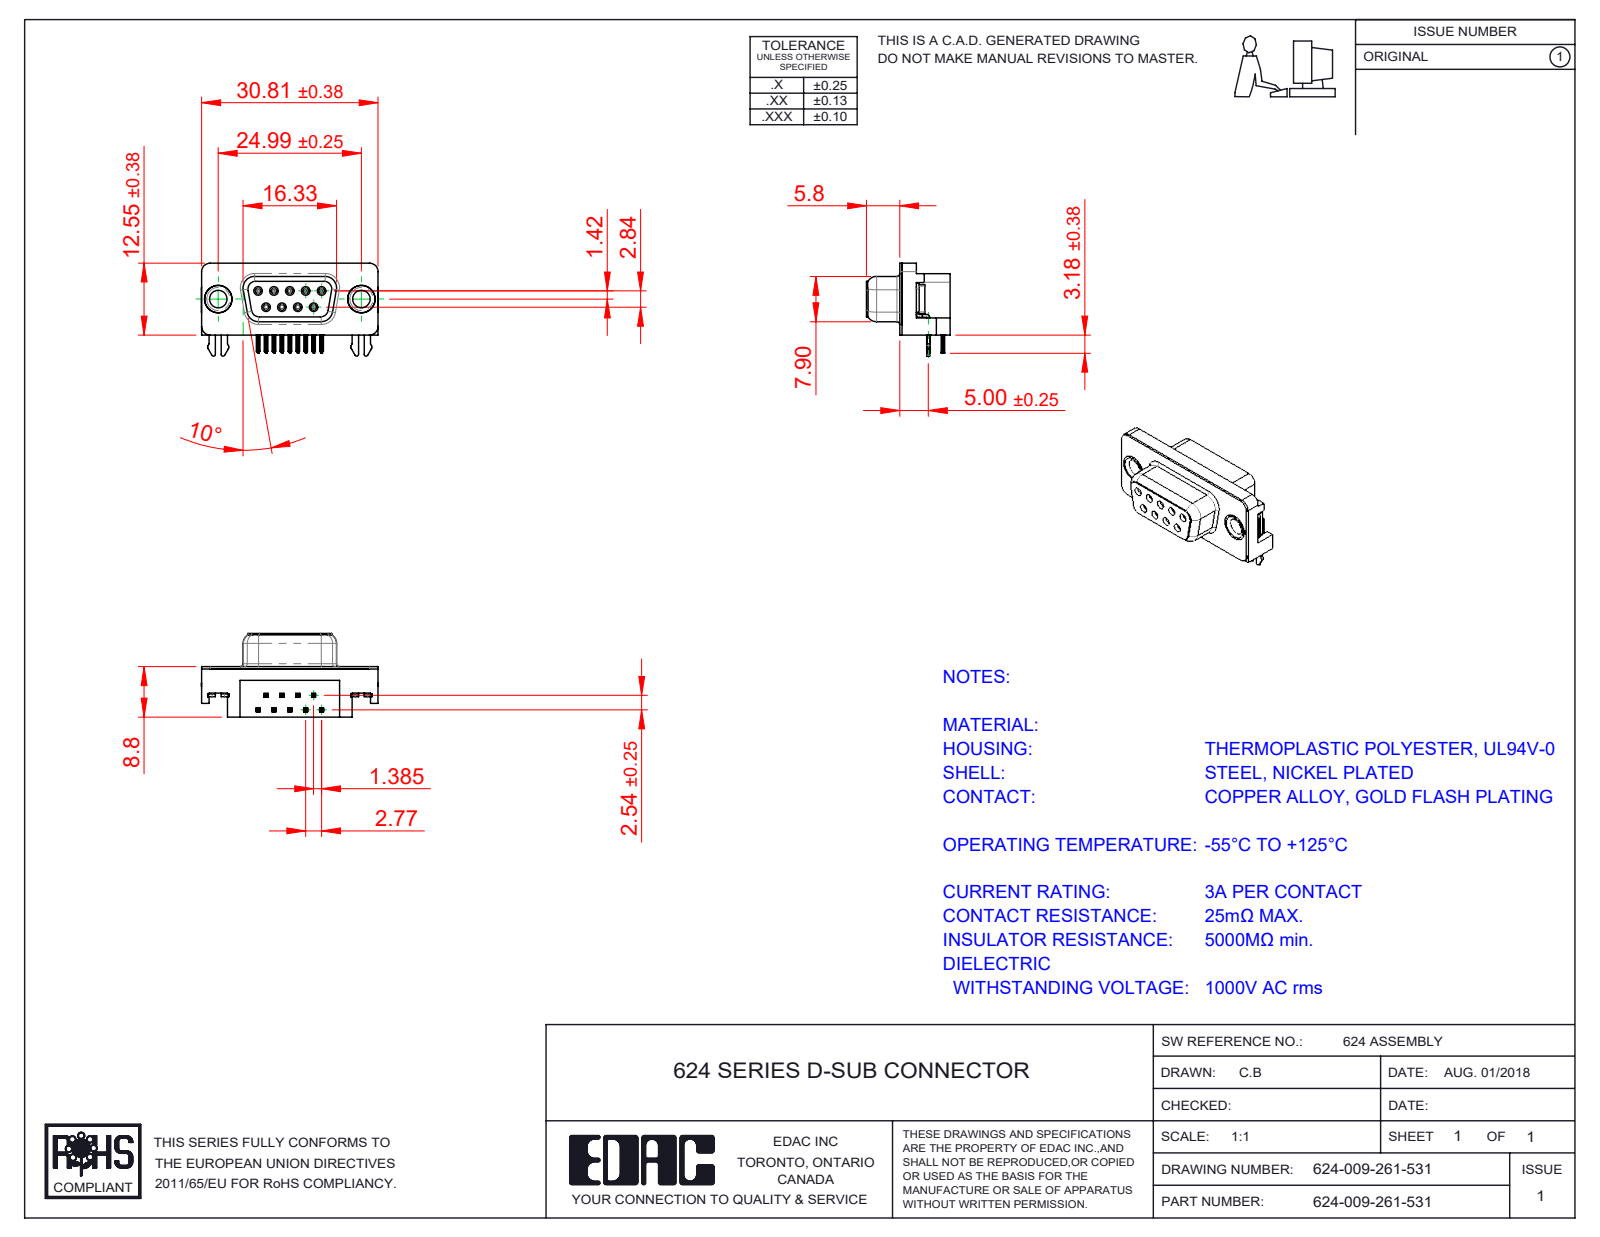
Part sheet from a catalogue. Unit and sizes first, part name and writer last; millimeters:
Units: millimetres
Overall size (bounding box): 30.89 × 16.25 × 14.6
Round holes (diameter × count): ⌀0.8 ×9, ⌀0.9 ×9, ⌀3.05 ×2, ⌀4 ×2, ⌀4.8 ×2, ⌀5 ×2
Round bosses / shafts (diameter × count): ⌀1.2 ×9, ⌀4.9 ×2, ⌀4.75 ×2, ⌀3.85 ×2
Partial cylindrical surfaces — rounded edges, fillets, slot ends (radius × count): R0.1 ×72, R0.15 ×36, R0.35 ×18, R0.5 ×10, R1 ×10, R0.34 ×9, R0.25 ×8, R1.35 ×8
Main face-to-face distances: 0.4, 8.4, 8.8, 2.9, 2.5, 6.2, 5.9, 0.35, 0.85, 10.69
Hole centre spacings: 3.16, 2.77, 5.54, 5.03, 5.04, 8.31, 7.48, 7.49
Volume: 2 934 mm³ · Surface area: 4 373 mm²
Bodies: 15 solids, 1512 faces (670 planar, 392 cylindrical, 450 other)
Part name (STEP PRODUCT): 624 Shell_9 Socket; 624 Housing_9 Socket; 624-009-261-531; 624 Thru Hole Rivet (+3 more)
STEP written by: SolidWorks 2016 (CONFIG_CONTROL_DESIGN)
